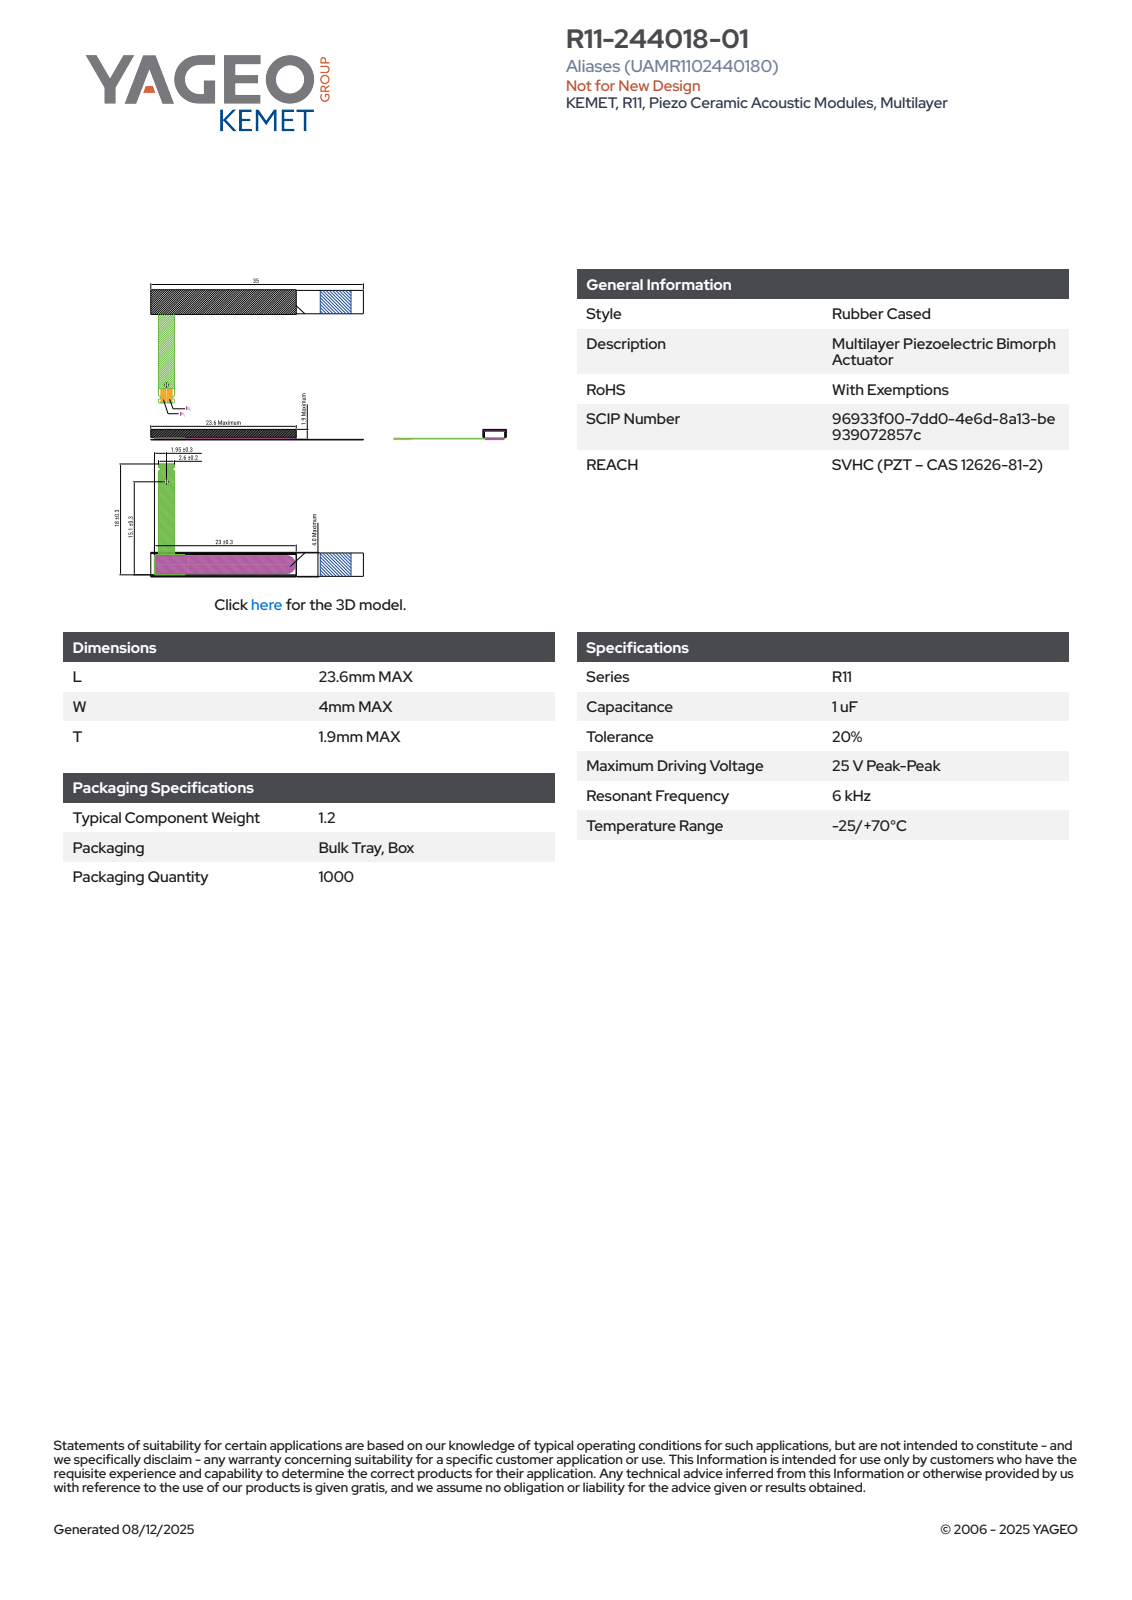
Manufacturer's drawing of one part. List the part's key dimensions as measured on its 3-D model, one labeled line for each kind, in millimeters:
Part name (STEP PRODUCT): PAM_KR11_L23.6W4T1.9
STEP written by: SolidWorks 2014 (AUTOMOTIVE_DESIGN)
Units: millimetres
Bodies: 1 solid, 84 faces (78 planar, 2 cylindrical, 4 other)
Overall size (bounding box): 35 × 18.3 × 1.9
Volume: 187 mm³ · Surface area: 455 mm²
Round holes (diameter × count): ⌀0.83 ×1
Main face-to-face distances: 1.9, 1.8, 4, 23.6, 0.85, 22.75, 3.65, 2.8, 19.95, 3.69
